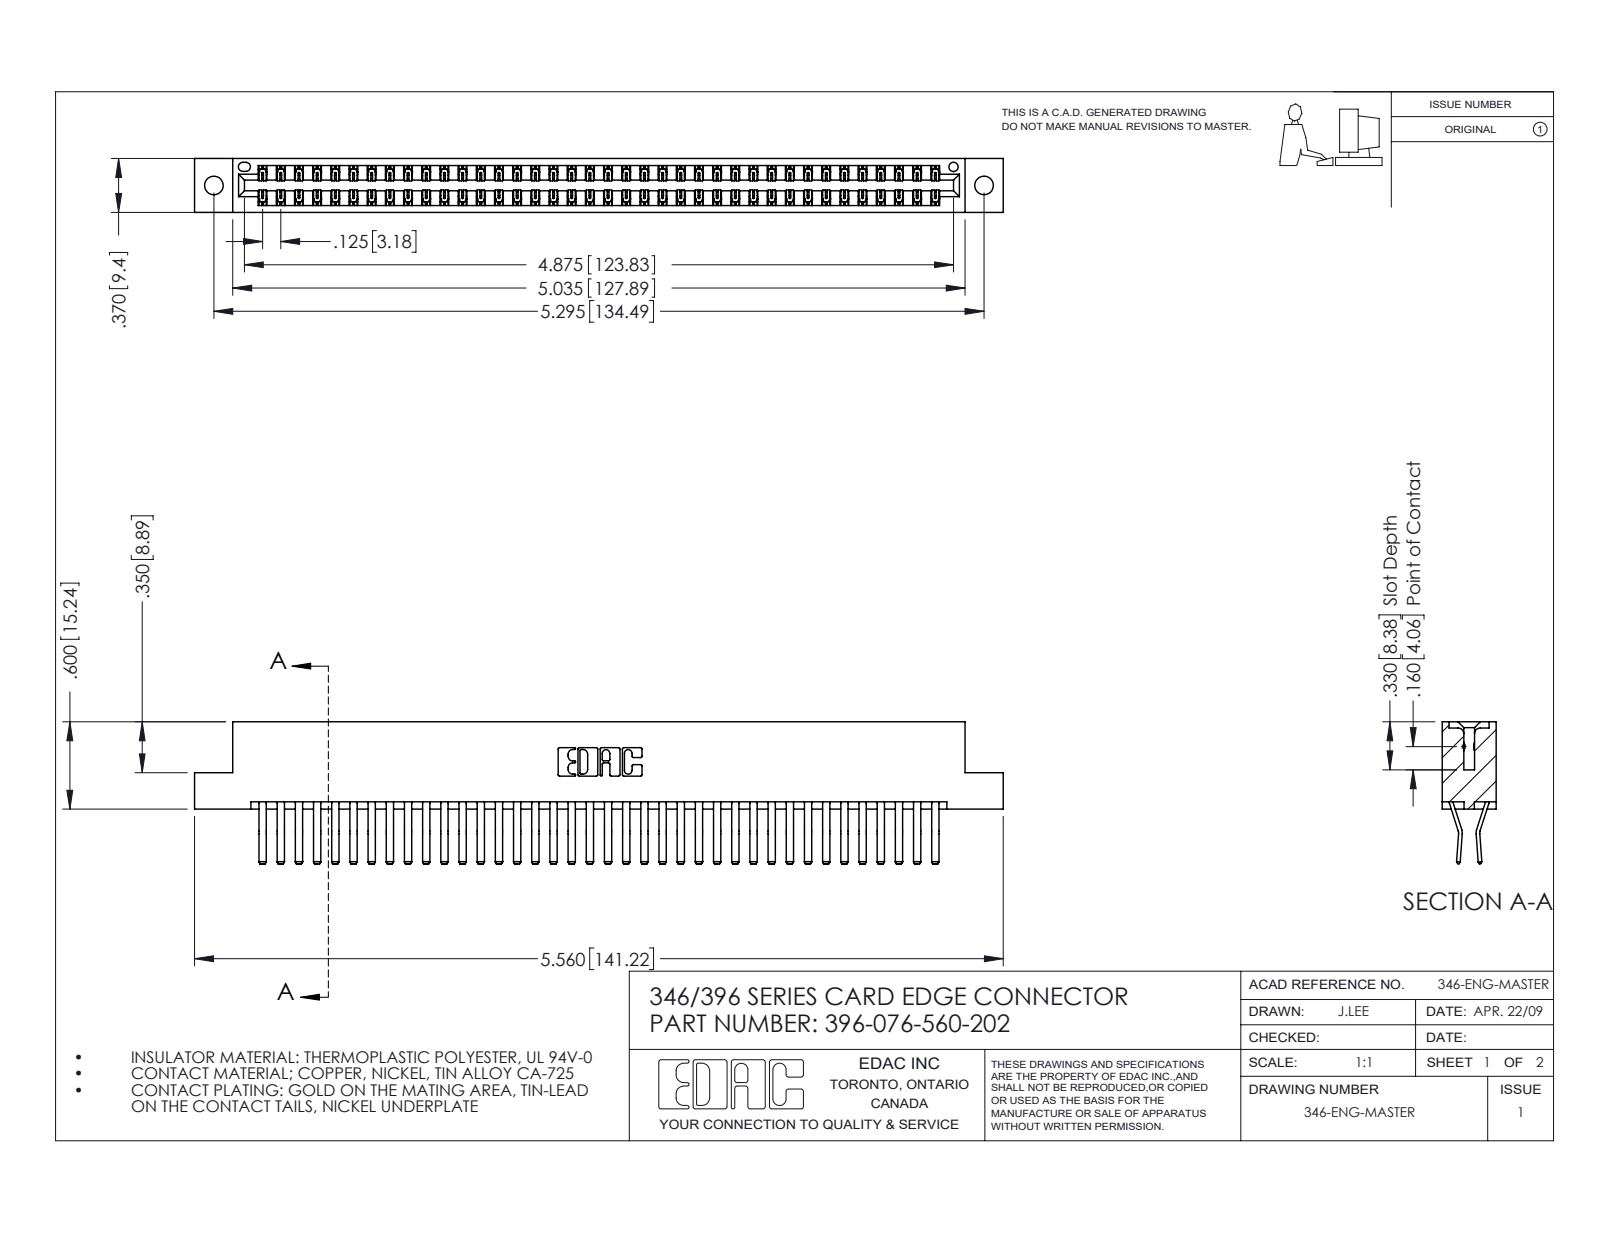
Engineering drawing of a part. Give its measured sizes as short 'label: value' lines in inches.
name: 346 Part_Flush Mounting Lugs - 0.128 Dia; 345-292-001_560 Tail; 396-076-560-202
written by: SolidWorks 2016 (CONFIG_CONTROL_DESIGN)
unit: in
bodies: 77 solids, 4226 faces (2736 planar, 1490 cylindrical, 0 other)
size: 5.56 × 0.975 × 0.37
volume: 0.867 in³; area: 31.8 in²
holes: 2× ⌀0.128, 1× ⌀0.064
rounds: 114× R0.006, 22× R0.01, 6× R0.007, 6× R0.031, 3× R0.026, 2× R0.01, 2× R0.014, 2× R0.022
face distances: 0.048, 0.322, 0.37, 0.025, 0.25, 0.072, 0.298, 0.275, 0.148, 0.222
hole spacings: 0.246, 5.086, 5.295
